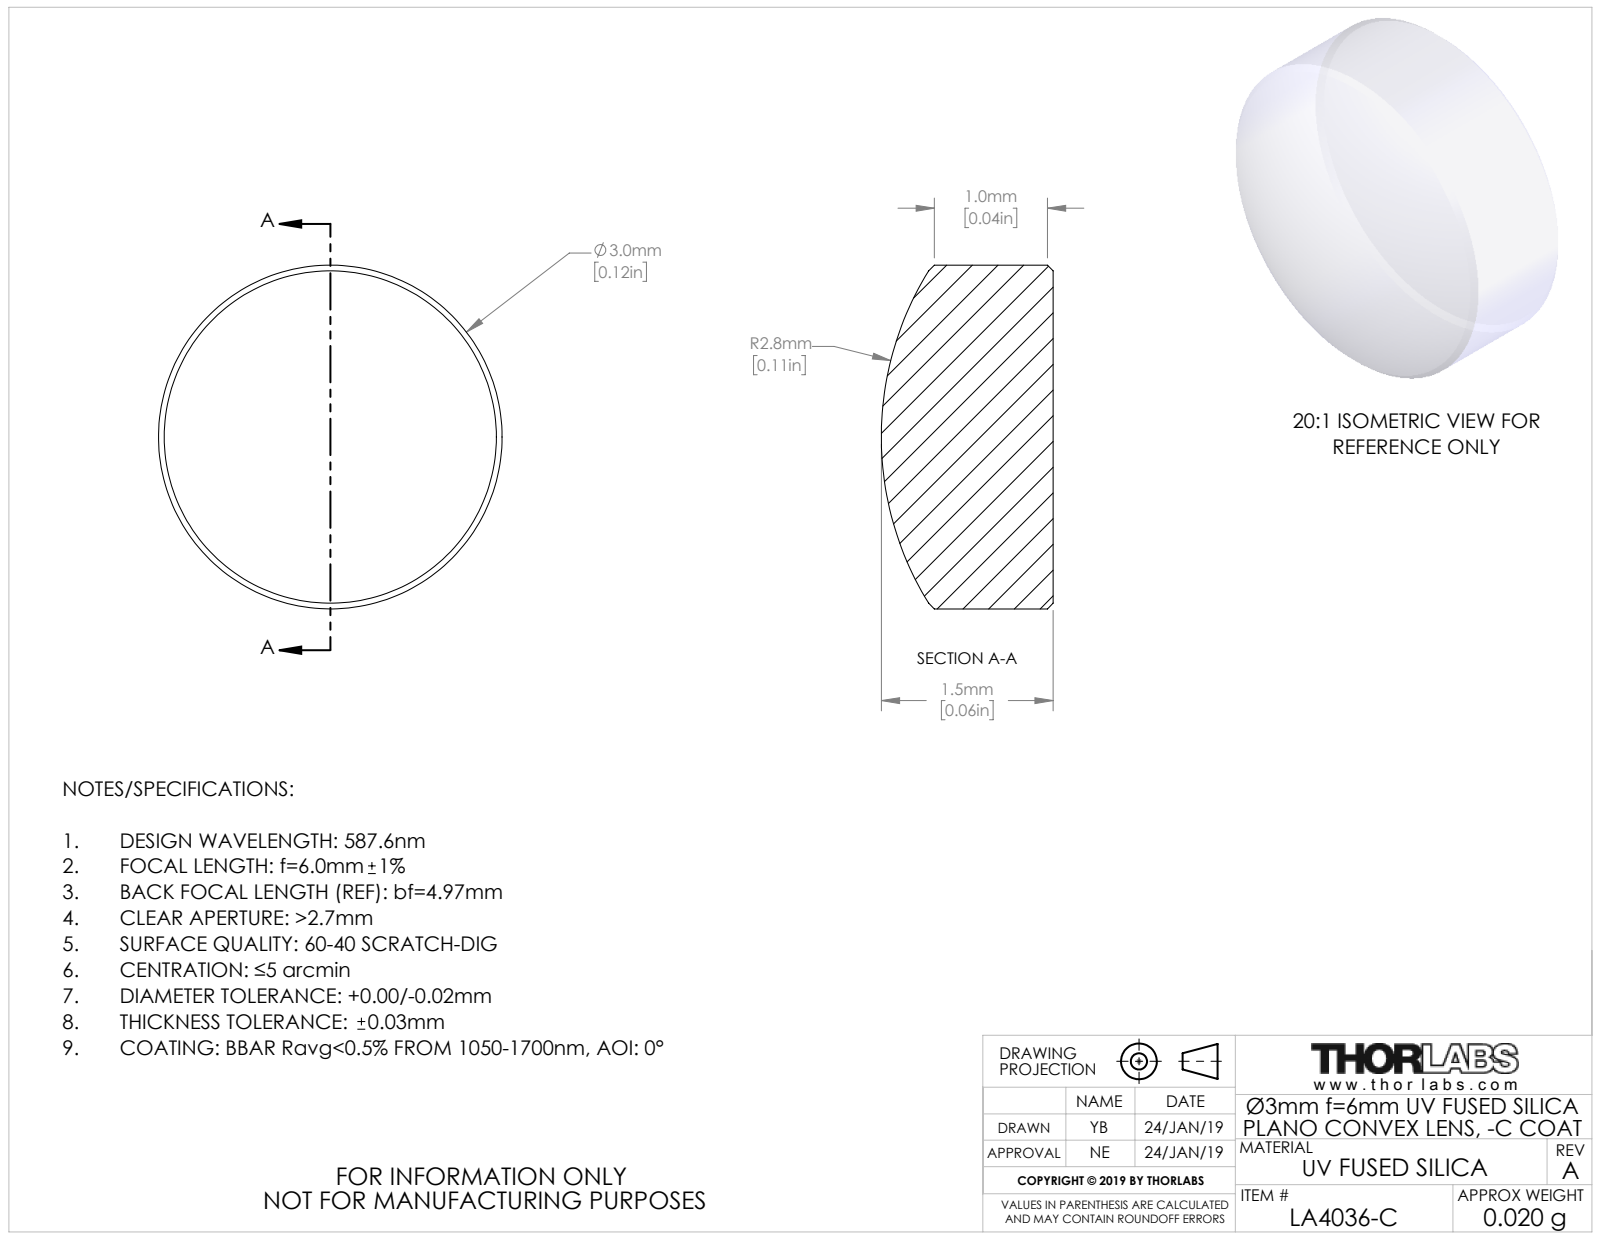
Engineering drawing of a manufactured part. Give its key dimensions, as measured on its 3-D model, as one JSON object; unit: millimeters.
{"part_name": "TTN162822-E0W", "step_written_by": "SolidWorks 2018 (CONFIG_CONTROL_DESIGN)", "units": "millimeters", "bodies": {"solids": 1, "faces": 9, "planar": 1, "cylindrical": 2, "other": 6}, "overall_size": [3, 3, 1.5], "volume_mm3": 9, "surface_area_mm2": 24, "round_bosses_or_shafts": [[3, 1]]}
